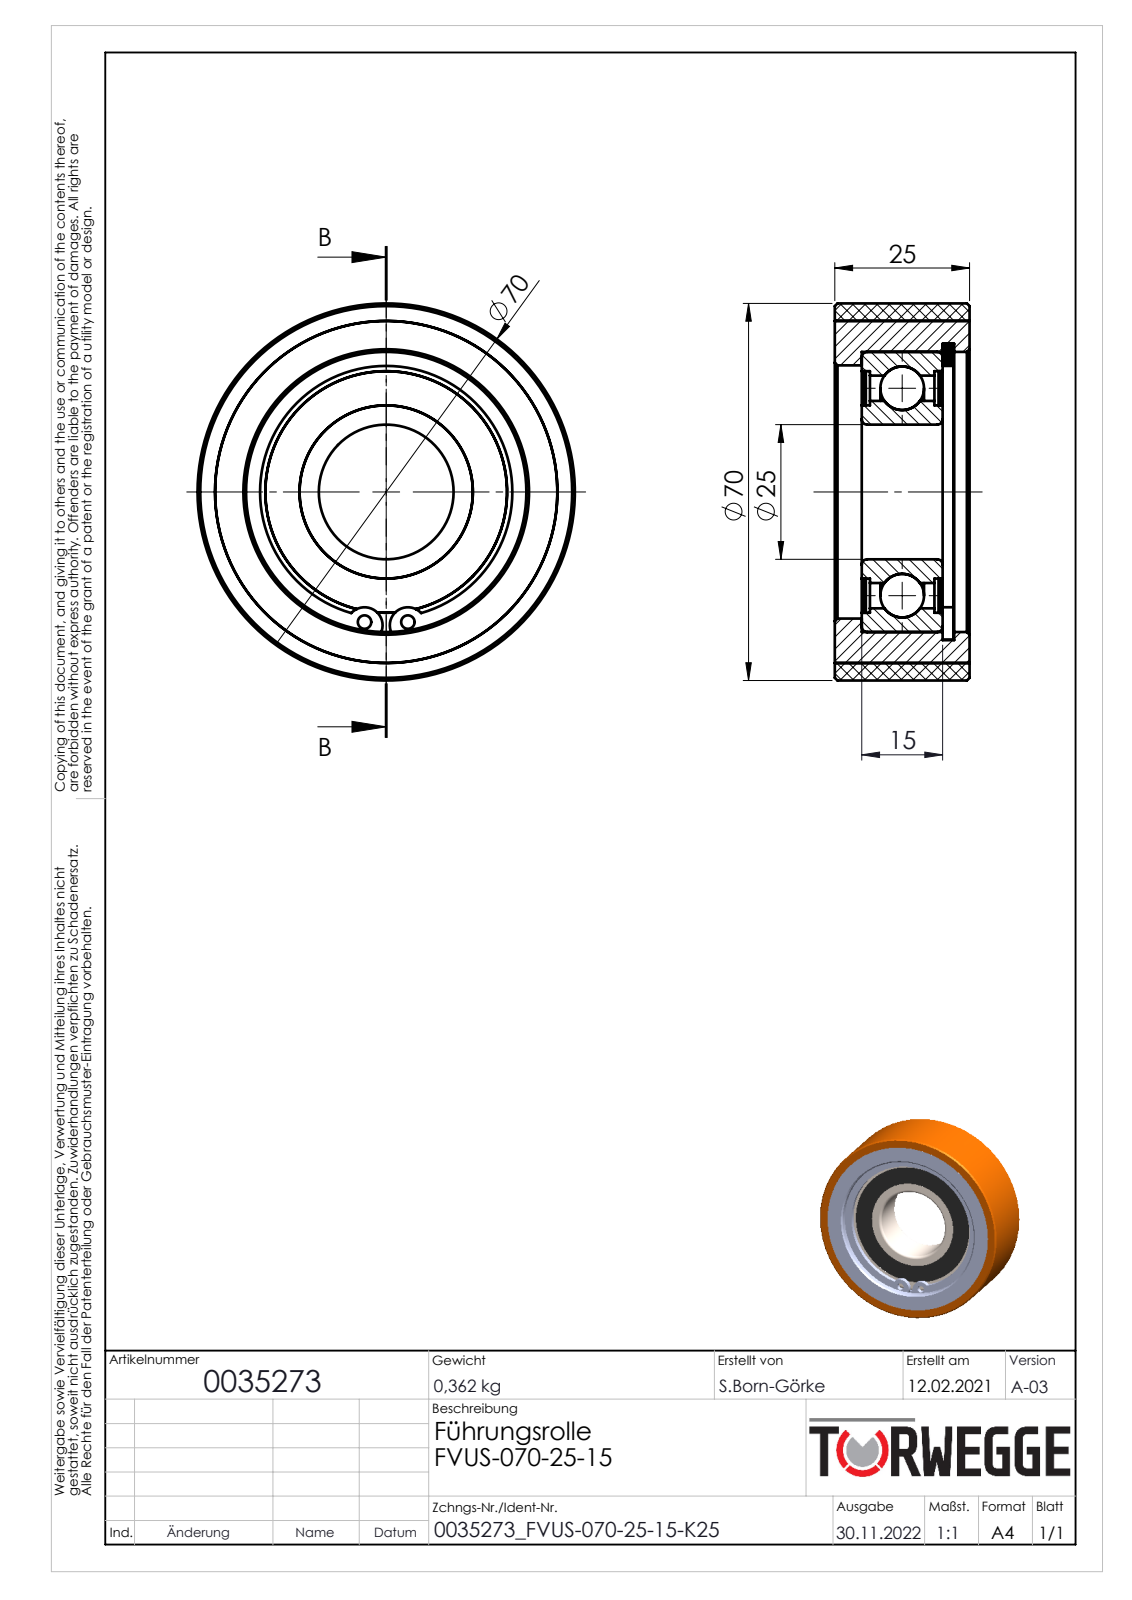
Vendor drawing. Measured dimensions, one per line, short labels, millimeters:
name: 0035273
written by: SolidWorks 2020 (AUTOMOTIVE_DESIGN)
unit: mm
bodies: 8 solids, 102 faces (21 planar, 55 cylindrical, 26 other)
size: 70 × 70 × 25
volume: 66 483 mm³; area: 41 955 mm²
holes: 2× ⌀2.5, 1× ⌀25, 1× ⌀32.16, 1× ⌀43.2, 1× ⌀44.85, 1× ⌀46.8, 1× ⌀47, 1× ⌀52, 1× ⌀55, 1× ⌀63.5
bosses: 1× ⌀70, 1× ⌀33.8
rounds: 2× R3.35
face distances: 20, 5, 0.76, 15, 5.76, 19.24, 14.24, 25, 13.48, 22
hole spacings: 24.48, 8.04
